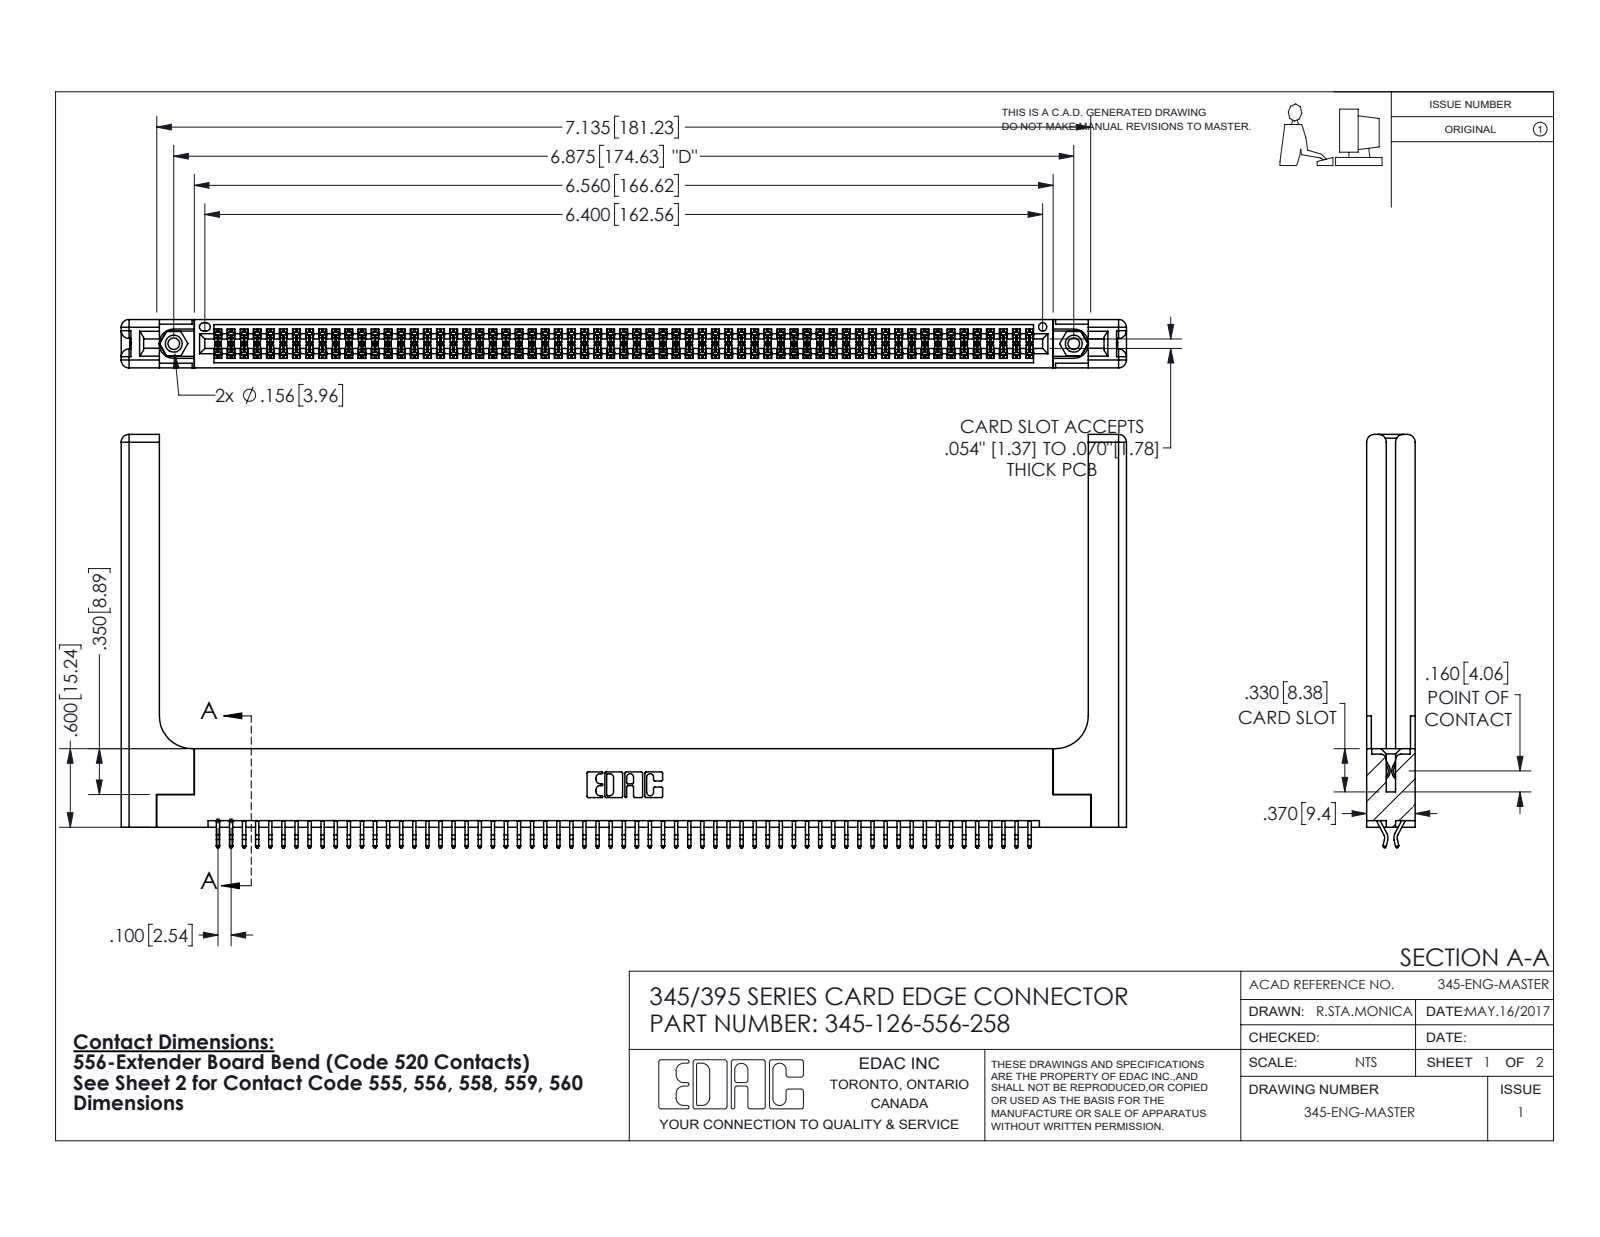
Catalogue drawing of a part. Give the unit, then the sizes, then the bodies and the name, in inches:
Units: inches
Overall size (bounding box): 7.679 × 3.157 × 0.37
Round holes (diameter × count): ⌀0.089 ×2, ⌀0.125 ×2, ⌀0.156 ×2, ⌀0.064 ×1
Round bosses / shafts (diameter × count): ⌀0.155 ×2
Partial cylindrical surfaces — rounded edges, fillets, slot ends (radius × count): R0.006 ×189, R0.01 ×22, R0.06 ×16, R0.007 ×6, R0.031 ×6, R0.026 ×3, R0.01 ×2, R0.014 ×2
Main face-to-face distances: 0.072, 0.298, 0.37, 0.2, 0.025, 0.098, 0.272, 0.225, 0.148, 0.15
Hole centre spacings: 0.27, 6.639, 6.875
Volume: 1.685 in³ · Surface area: 52.15 in²
Bodies: 131 solids, 7438 faces (4890 planar, 2488 cylindrical, 60 other)
Part name (STEP PRODUCT): 345-126-556-258; 345-250-001_345-250-001-102; 345-292-001_556 Tail; 345 Part_Flush Mounting Lugs - 0.156 Dia-TH (+1 more)
STEP written by: SolidWorks 2016 (CONFIG_CONTROL_DESIGN)
